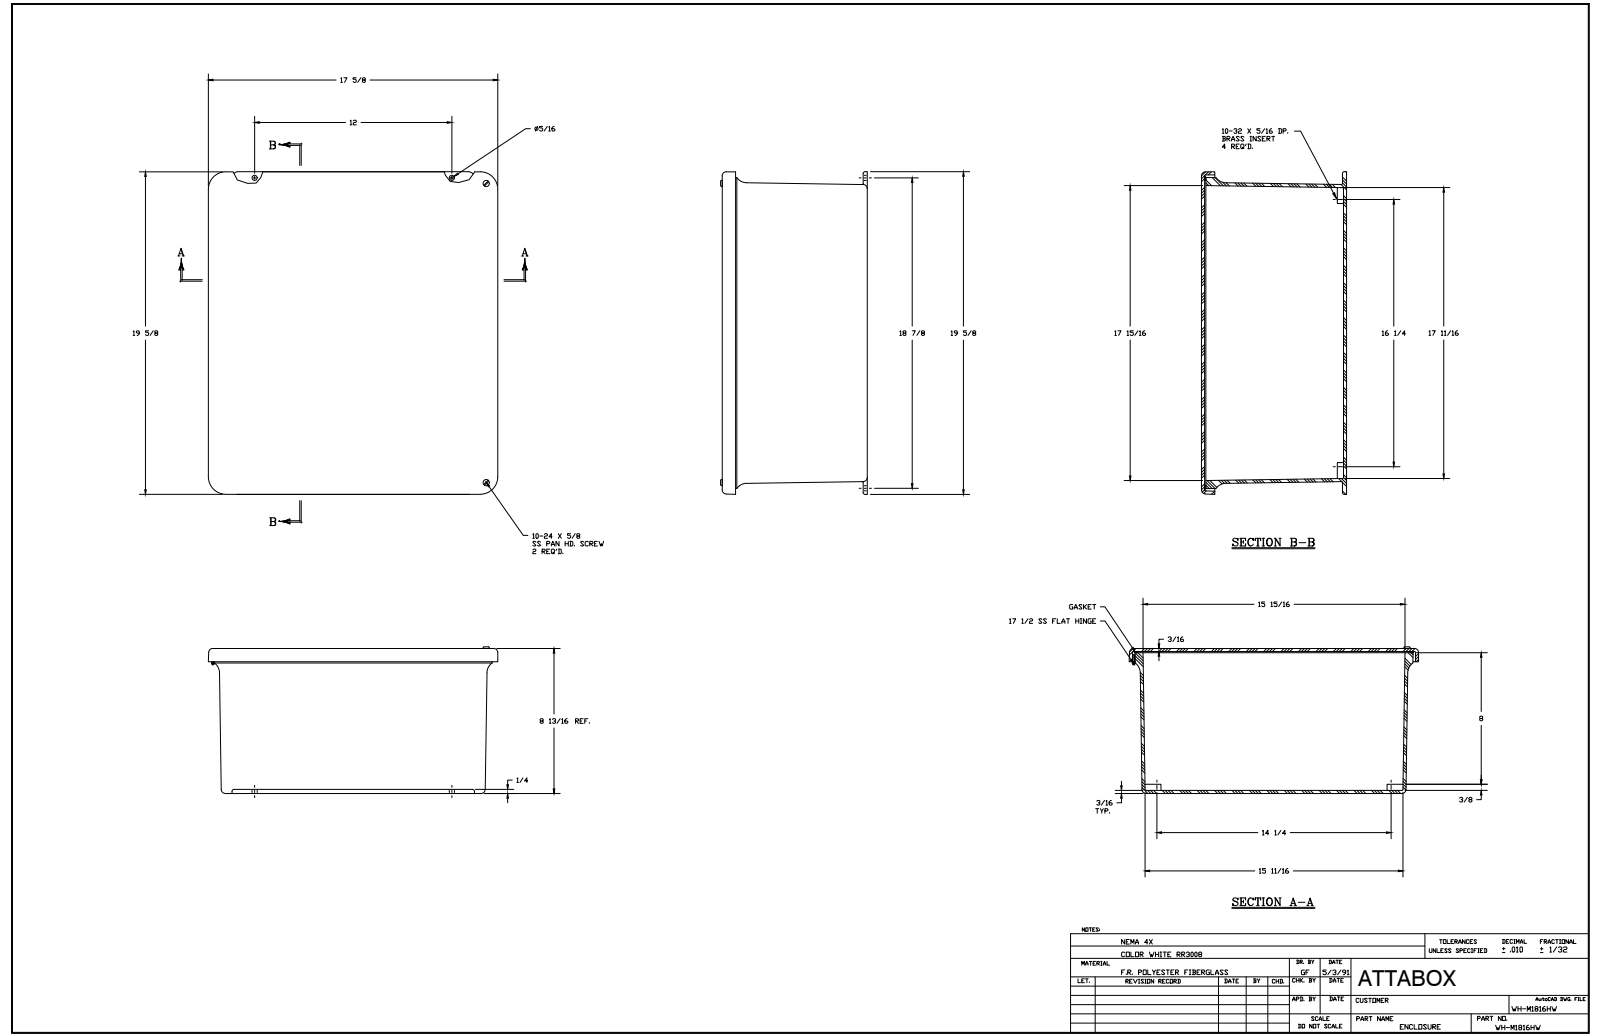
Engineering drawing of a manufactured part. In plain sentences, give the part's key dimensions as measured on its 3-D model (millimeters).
The part is named "WH-M1816HW". Its 3-D file was written by "SolidWorks 2018 (AUTOMOTIVE_DESIGN)". It is 26 solids with 945 faces: 369 planar, 367 cylindrical and 209 other. Overall it measures 498.5 by 448.1 by 227.5 millimeters. Its volume is 4 254 000 cubic millimeters and its surface area 1 741 000 square millimeters. Round holes: 12 of diameter 3.3, 12 of diameter 3.6, 5 of diameter 3.9, 4 of diameter 4, 4 of diameter 5.5, 2 of diameter 3.7, 1 of diameter 2.2. Round bosses or shafts: 12 of diameter 6.4, 9 of diameter 3.2, 6 of diameter 6.9, 3 of diameter 3.2, 2 of diameter 4.8, 2 of diameter 4, 1 of diameter 3.9, 1 of diameter 3.9. Partial cylindrical surfaces (rounded edges, fillets, slot ends): 20 of radius 0.8, 12 of radius 3.2, 8 of radius 6.4, 4 of radius 5.1, 4 of radius 9.5, 4 of radius 19.1, 2 of radius 1.6. The main face-to-face distances are 4.7, 219.4, 224.2, 4.8, 214.6, 219.4, 12.4, 7.7, 217.5, 212.7. The hole center spacings are 85.7, 85.7, 171.5, 260.4, 6.4, 247.7, 254, 34.8.
